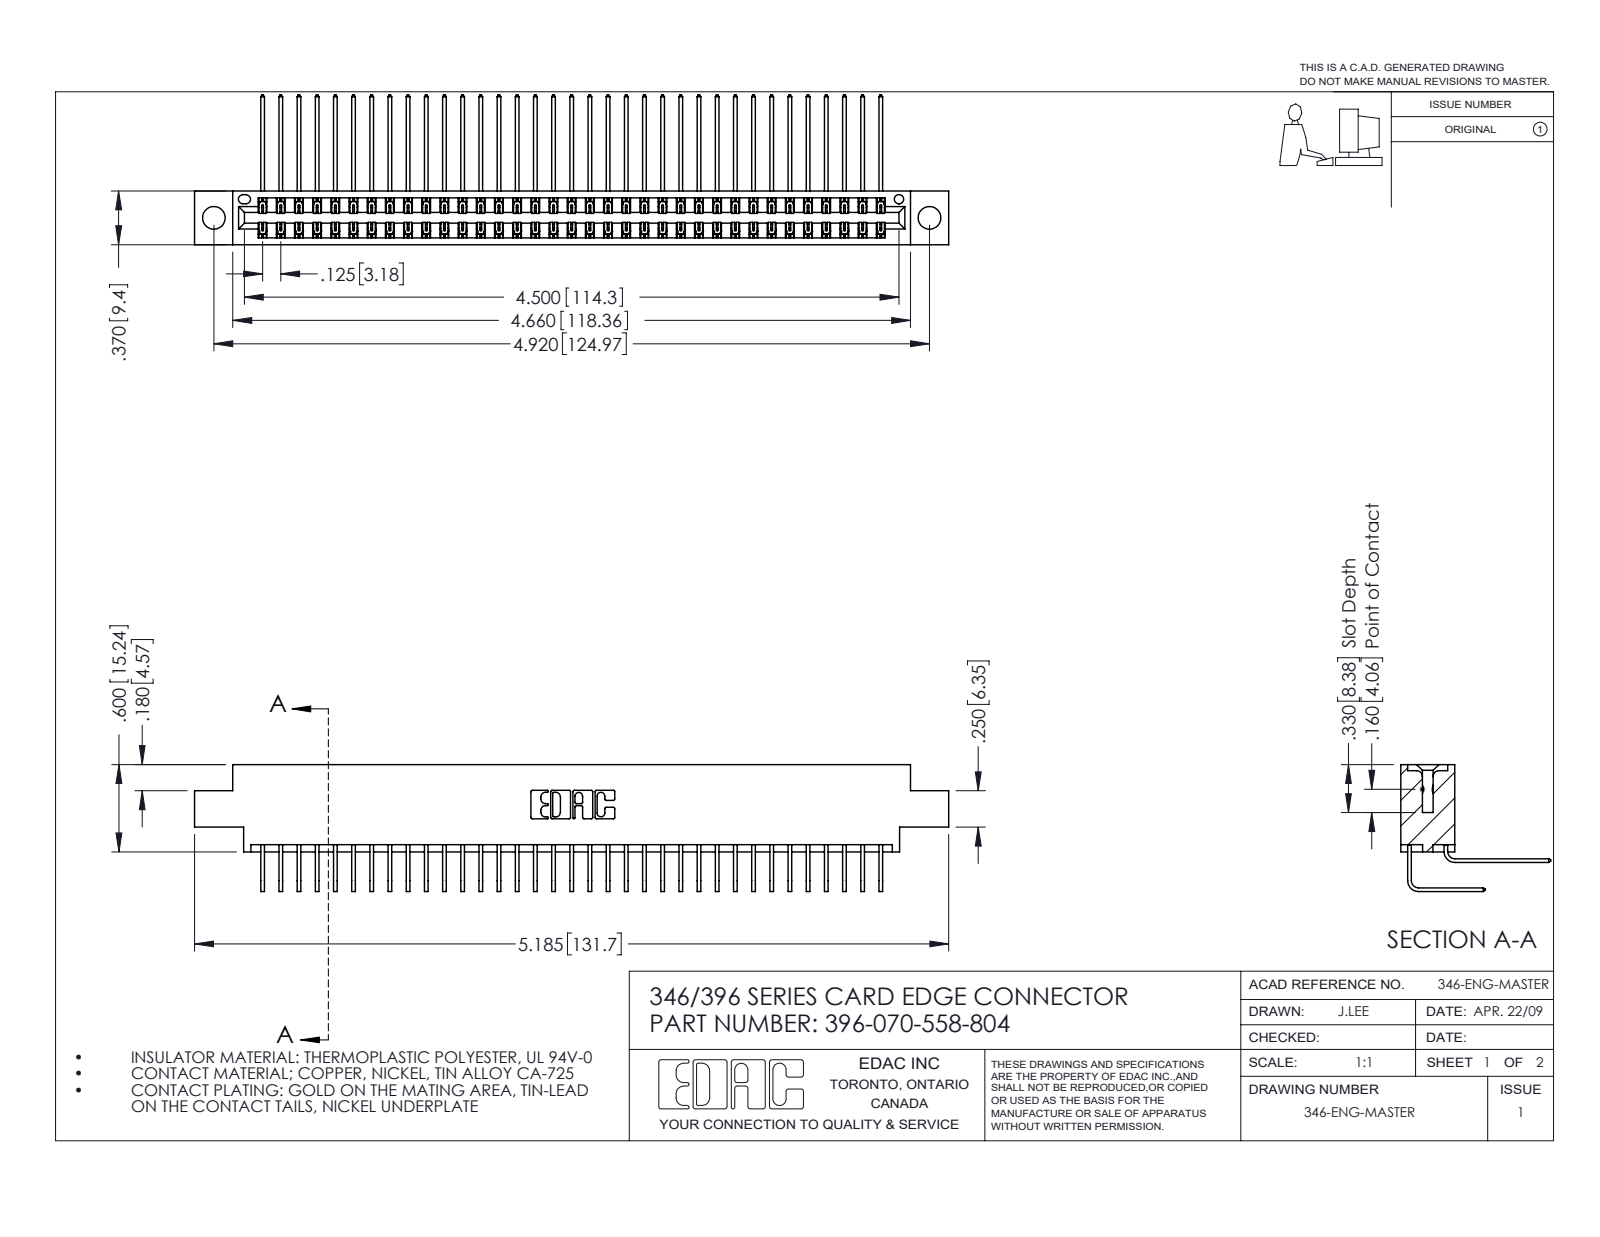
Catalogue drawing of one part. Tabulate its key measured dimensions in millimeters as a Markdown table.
| quantity | value |
| --- | --- |
| part name | 345-292-001_558 Tail - 2; 345-292-001_558 559 Tail - 1; 396-070-558-804; 346 Part_0.170 Offset - 0.156 Dia-TH |
| STEP written by | SolidWorks 2016 (CONFIG_CONTROL_DESIGN) |
| units | millimeters |
| bodies | 71 solids, 3906 faces (2670 planar, 1236 cylindrical, 0 other) |
| overall size | 131.7 × 26.2 × 22.2 |
| volume | 12 900 mm³ |
| surface area | 19 620 mm² |
| round holes (diameter × count) | 4 × 2, 1.6 × 1 |
| partial cylindrical surfaces (radius × count) | 0.2 × 105, 0.3 × 22, 0.2 × 6, 0.8 × 6, 0.7 × 3, 0.4 × 2, 0.6 × 2, 0.6 × 2 |
| main face-to-face distances | 8.2, 1.2, 0.6, 9.4, 6.4, 7.6, 1.8, 7, 3.8, 5.6 |
| hole center spacings | 6.2, 119.7, 125 |
